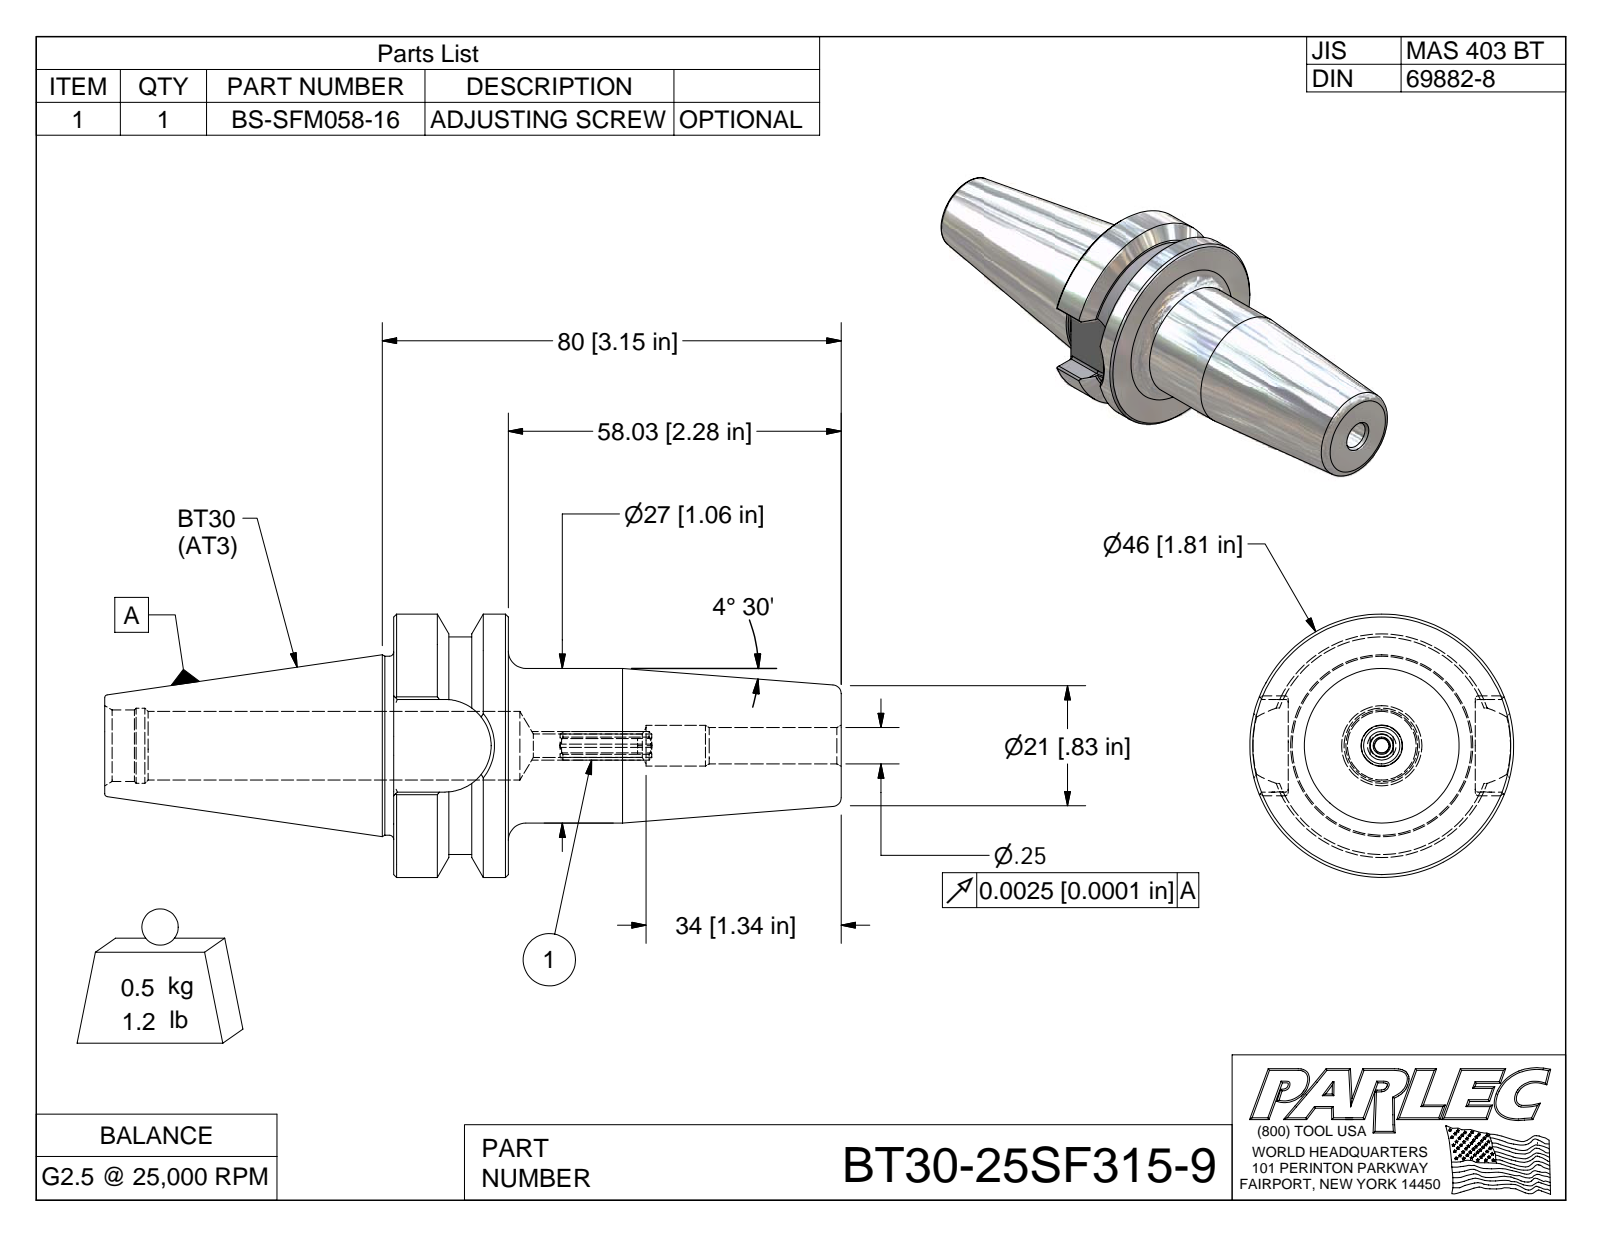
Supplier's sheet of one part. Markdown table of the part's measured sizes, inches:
| quantity | value |
| --- | --- |
| part name | BT30-25SF315-9; BT30-25SF315-9-1; BS-SFM058-16 |
| STEP written by | Autodesk Inventor 2009 (AUTOMOTIVE_DESIGN) |
| units | inches |
| bodies | 2 solids, 92 faces (35 planar, 22 cylindrical, 35 other) |
| overall size | 5.056 × 1.811 × 1.811 |
| volume | 4.411 in³ |
| surface area | 28.41 in² |
| round holes (diameter × count) | 0.25 × 1, 0.28 × 1, 0.517 × 1 |
| round bosses / shafts (diameter × count) | 1.811 × 1, 1.23 × 1, 1.063 × 1 |
| partial cylindrical surfaces (radius × count) | 0.02 × 8, 0.098 × 1, 0.319 × 1, 0.748 × 1 |
| main face-to-face distances | 0.787, 1.283, 3.072, 2.285, 0.563, 0.72, 0.157, 1.984, 2.771, 5.056 |
